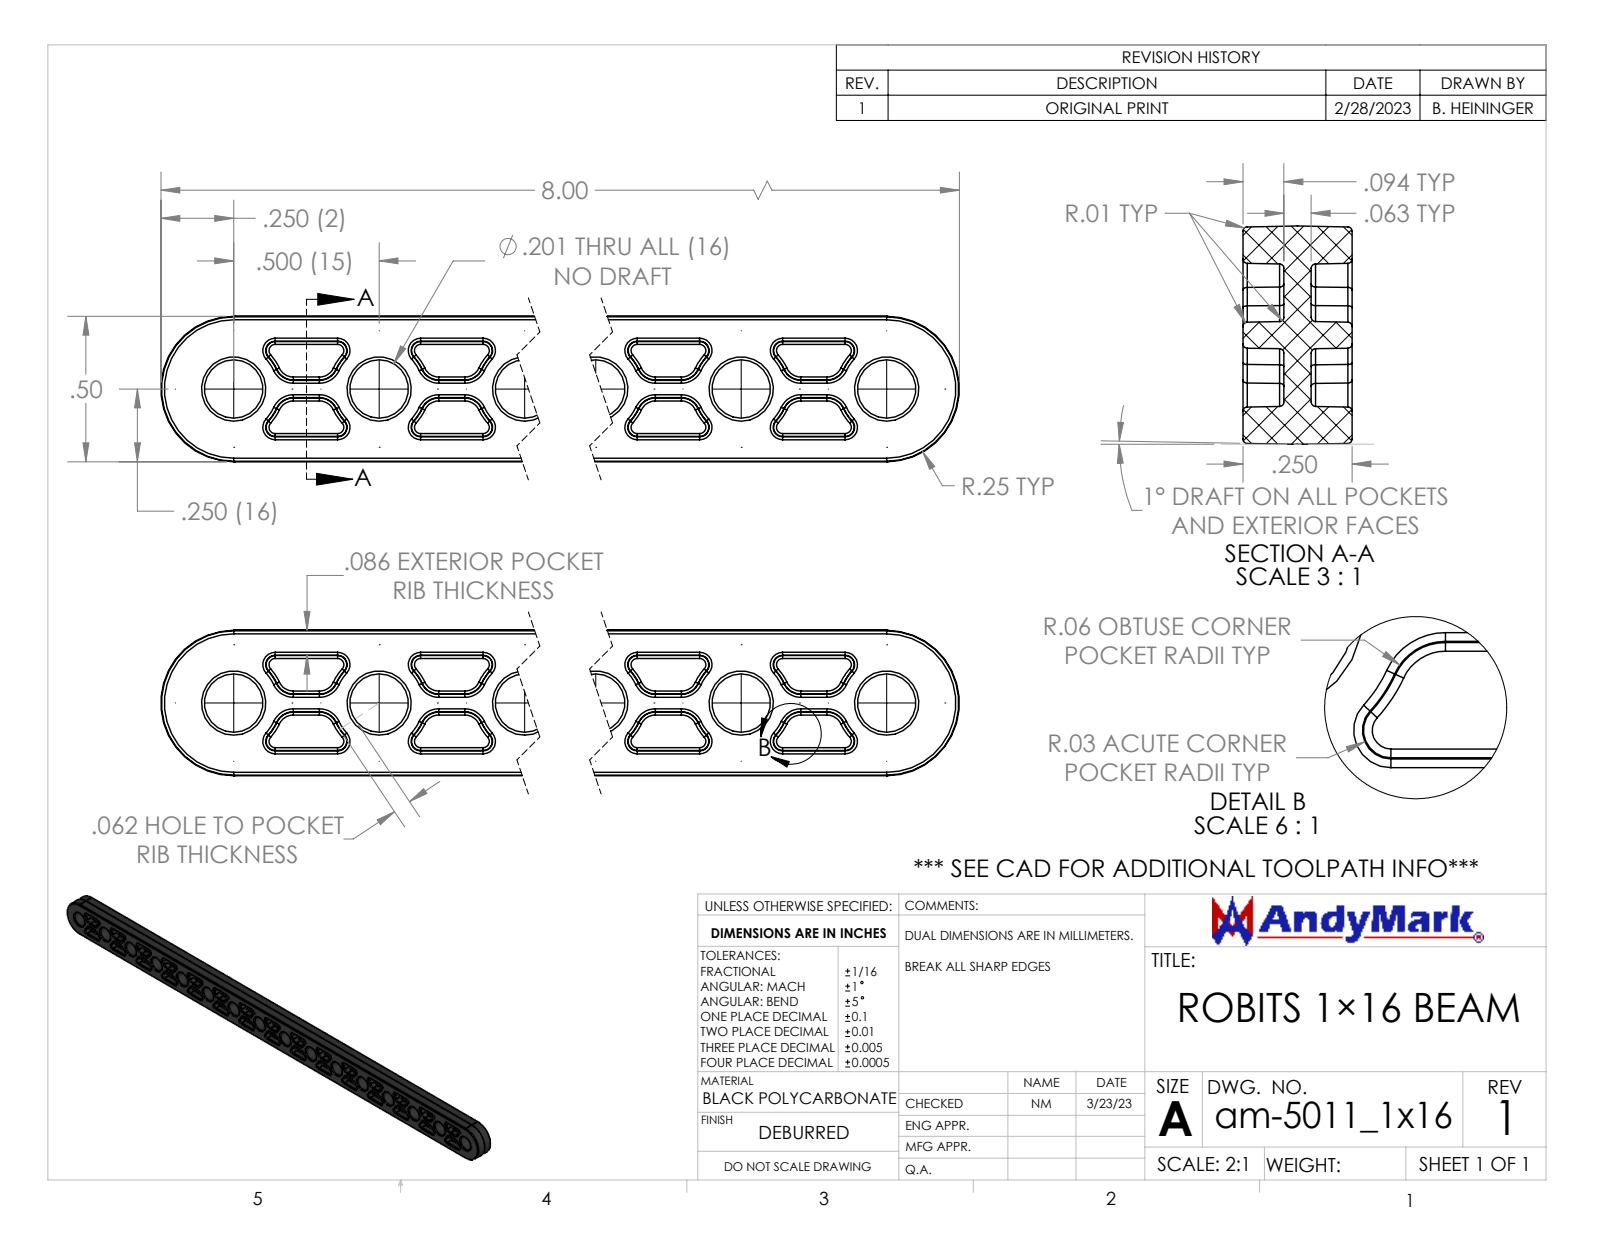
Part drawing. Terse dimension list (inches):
name: am-5011_1x16 RoBits 1×16 Beam
written by: SolidWorks 2022 (AUTOMOTIVE_DESIGN)
unit: in
bodies: 1 solid, 1618 faces (186 planar, 279 cylindrical, 1153 other)
size: 8 × 0.5 × 0.25
volume: 0.682 in³; area: 16.78 in²
holes: 16× ⌀0.201
rounds: 22× R0.01, 1× R0.163
face distances: 0.25, 0.5, 0.094, 0.156, 0.087, 0.413, 0.062, 0.325, 0.218, 0.282
hole spacings: 0.5, 1, 1.5, 2, 2.5, 3, 3.5, 4
